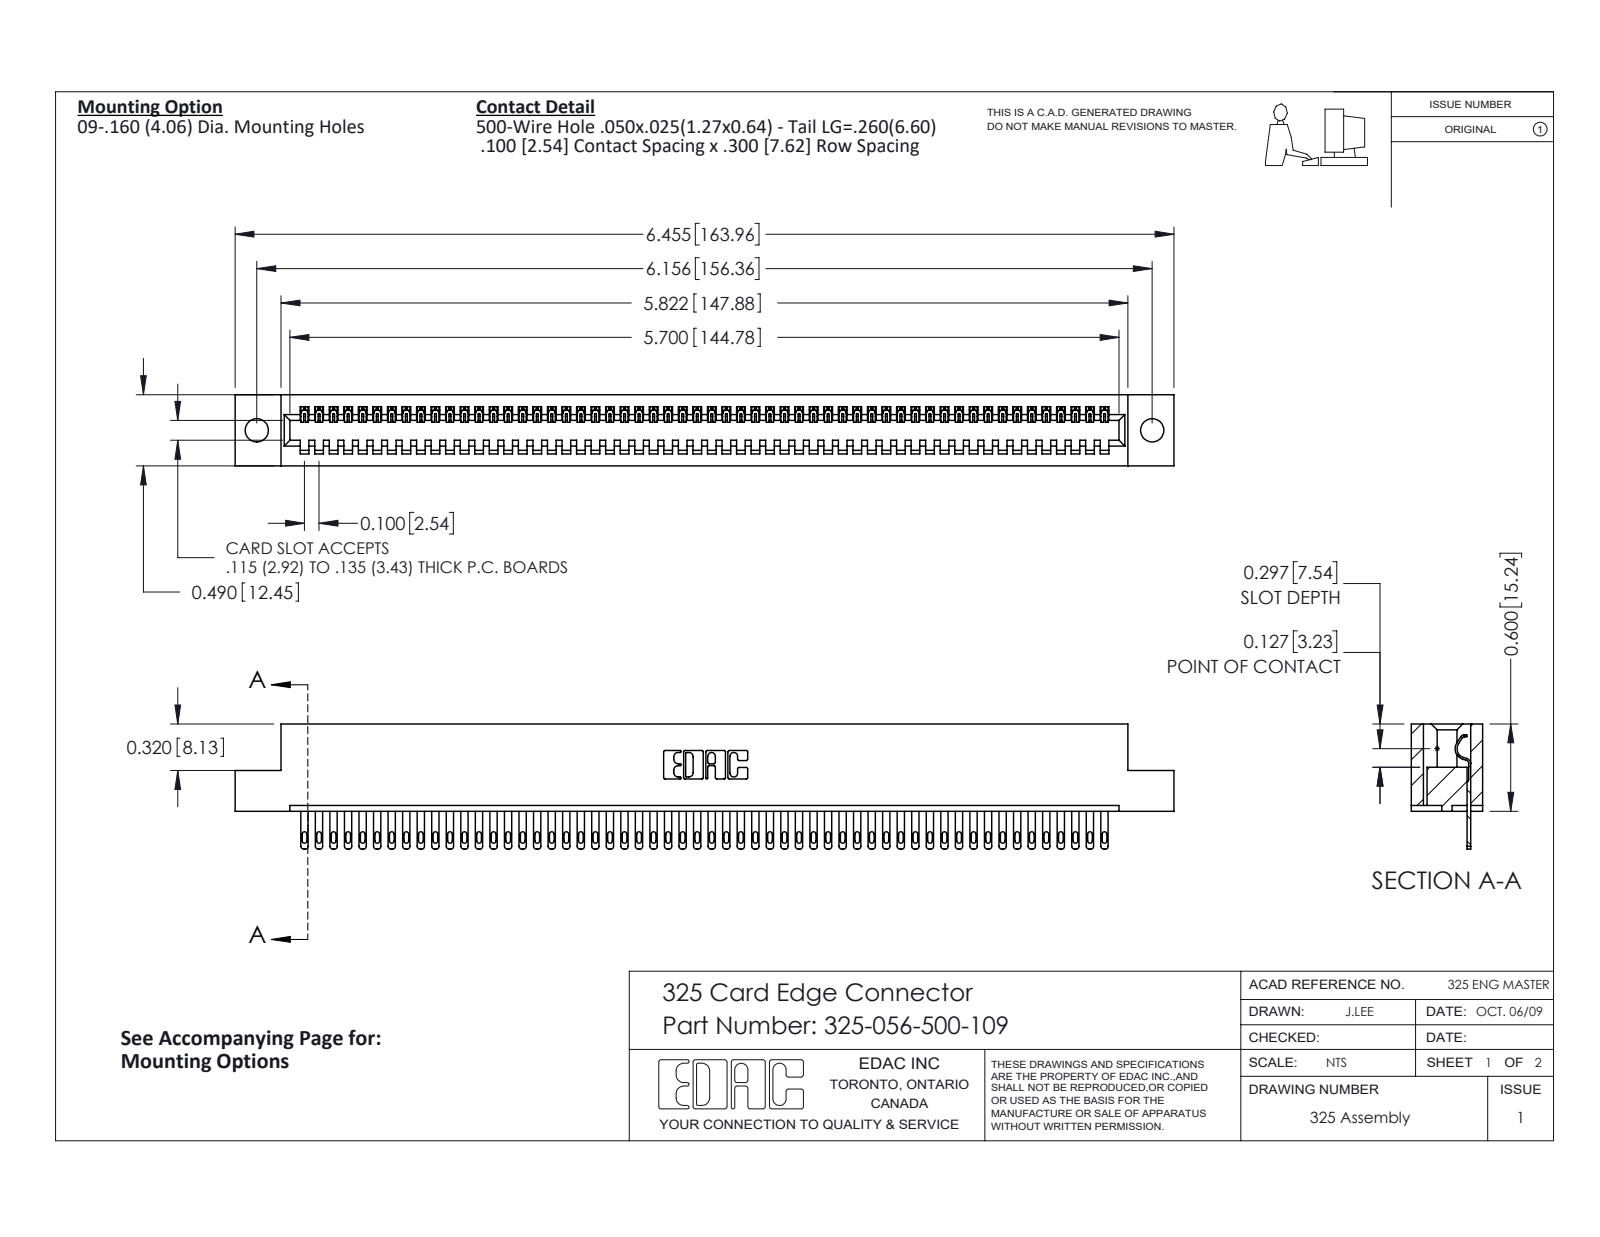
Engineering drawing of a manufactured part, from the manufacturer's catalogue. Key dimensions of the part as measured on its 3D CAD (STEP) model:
Part name (STEP PRODUCT): 325 Part_.160 TH; 325-056-500-109; 325-292-001_325-293-100
STEP written by: SolidWorks 2016 (CONFIG_CONTROL_DESIGN)
Units: inches
Bodies: 57 solids, 3138 faces (2086 planar, 1052 cylindrical, 0 other)
Overall size (bounding box): 6.455 × 0.86 × 0.49
Volume: 1.265 in³ · Surface area: 35.51 in²
Round holes (diameter × count): ⌀0.16 ×2
Partial cylindrical surfaces — rounded edges, fillets, slot ends (radius × count): R0.006 ×112, R0.016 ×112, R0.02 ×112, R0.01 ×22, R0.007 ×6, R0.031 ×6, R0.026 ×3, R0.014 ×1
Main face-to-face distances: 0.083, 0.407, 0.49, 0.107, 0.383, 0.025, 0.3, 0.325, 0.263, 0.56
Hole centre spacings: 6.156
